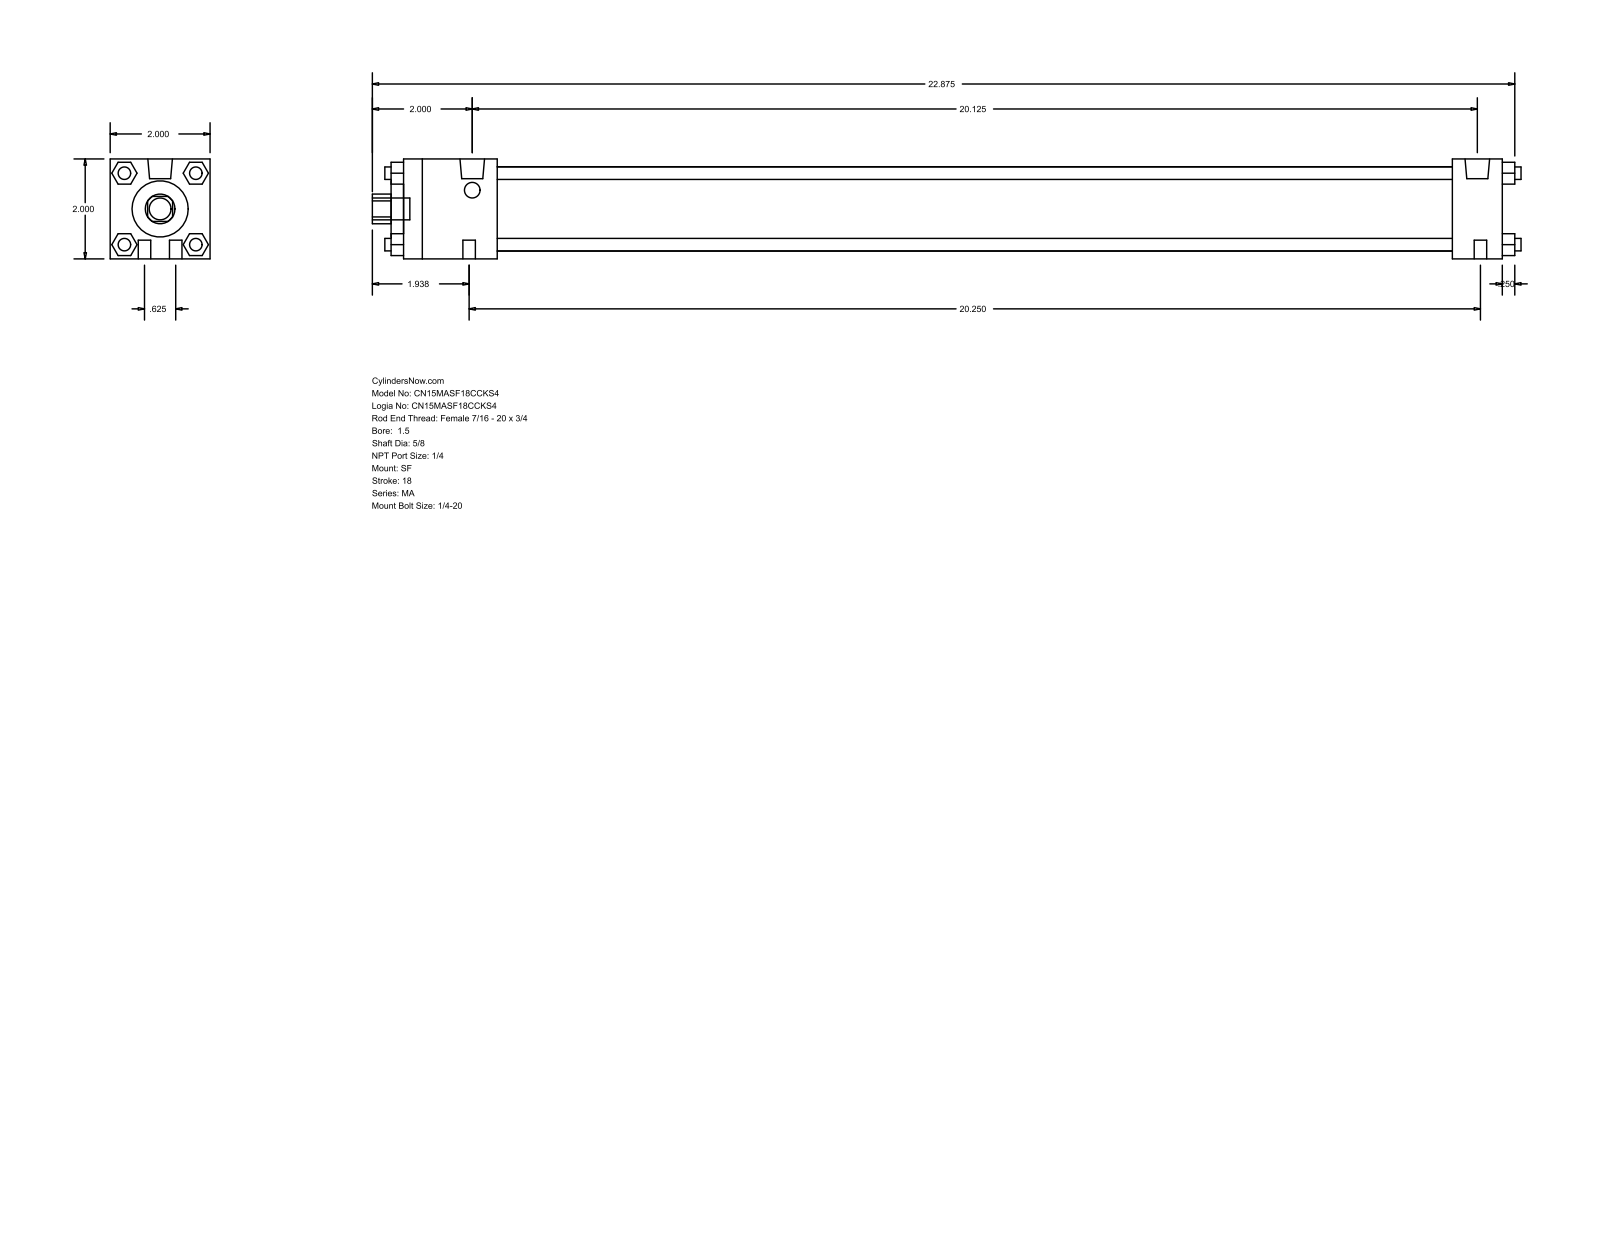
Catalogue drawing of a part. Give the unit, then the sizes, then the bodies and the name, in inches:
Units: inches
Overall size (bounding box): 23 × 2 × 2
Round holes (diameter × count): ⌀0.625 ×1, ⌀1.125 ×1, ⌀1.69 ×1
Round bosses / shafts (diameter × count): ⌀0.25 ×8, ⌀0.492 ×2, ⌀0.313 ×2, ⌀0.437 ×1
Partial cylindrical surfaces — rounded edges, fillets, slot ends (radius × count): R0.297 ×1
Main face-to-face distances: 2, 22, 0.25, 22.25, 1.875, 21, 19.125, 20.125, 1, 2.125
Bodies: 0 solids, 124 faces (94 planar, 30 cylindrical, 0 other)
Part name (STEP PRODUCT): MA_SF__0150_0.625
STEP written by: GSSL Pune (CONFIG_CONTROL_DESIGN)
